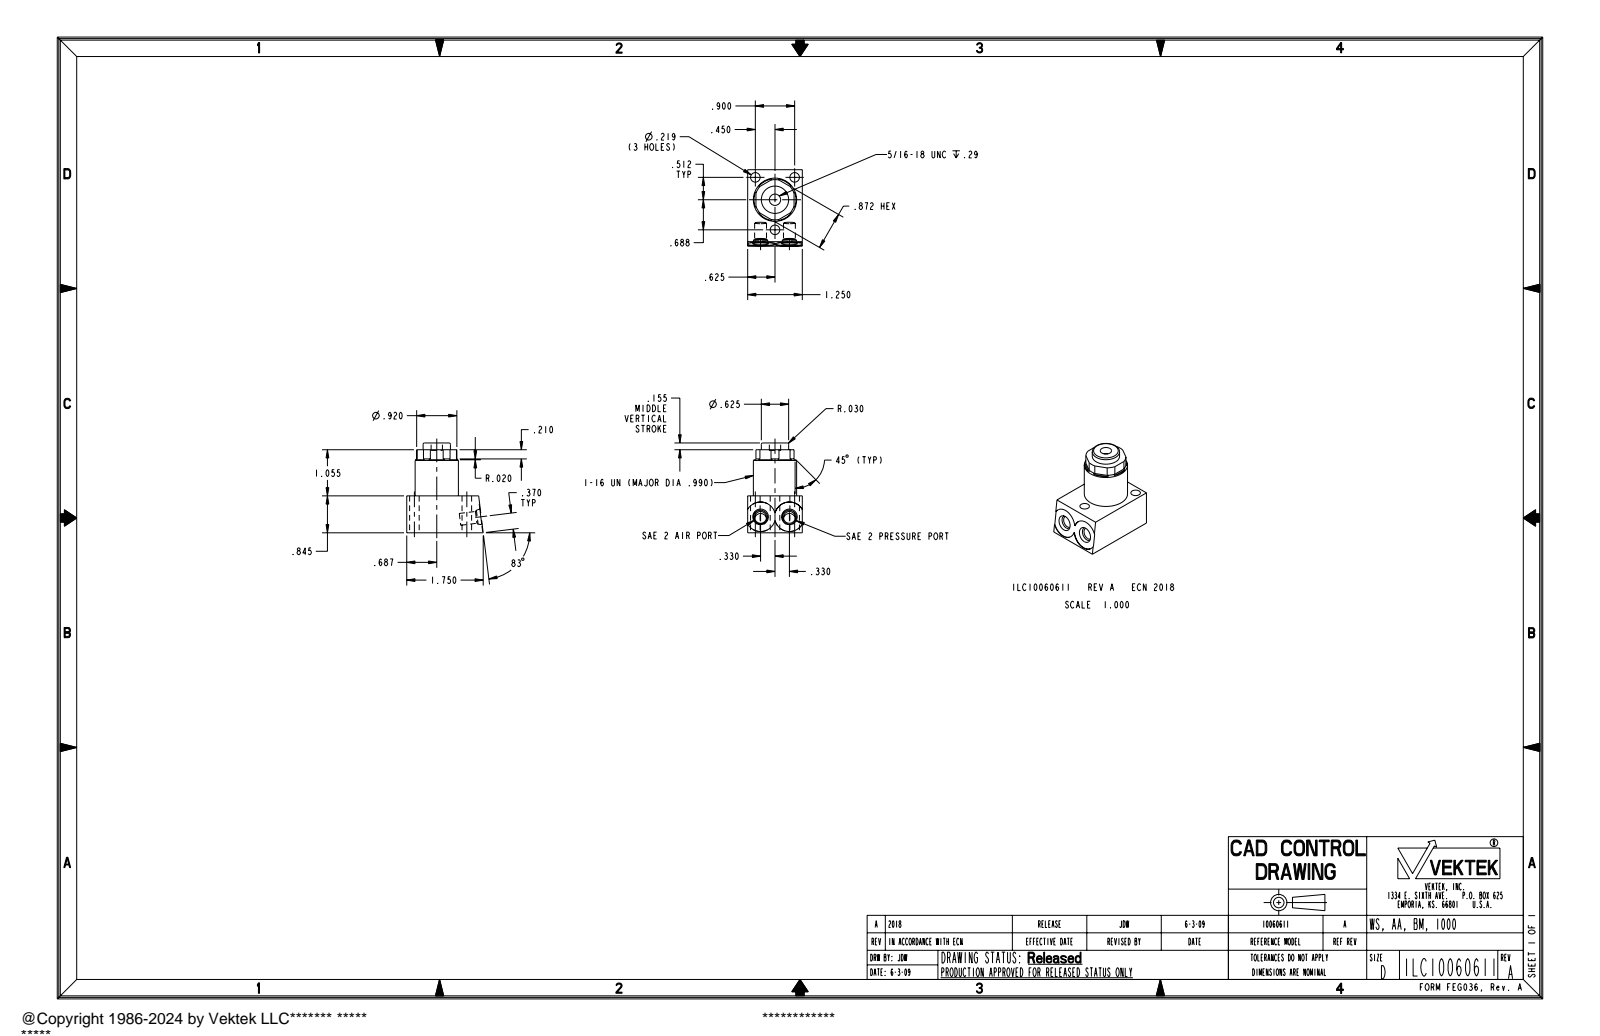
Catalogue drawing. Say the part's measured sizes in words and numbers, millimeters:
The part is named "ILC10060611". Its 3-D file was written by "PRO/ENGINEER BY PARAMETRIC TECHNOLOGY CORPORATION, 2007460 (AUTOMOTIVE_DESIGN_CC2)". It is 1 solid with 69 faces: 25 planar, 32 cylindrical and 12 other. Overall it measures 52.2 by 44.5 by 31.8 millimeters. Its volume is 40 130 cubic millimeters and its surface area 9 781 square millimeters. Round holes: 3 of diameter 5.6, 2 of diameter 6.9, 1 of diameter 6.6. Round bosses or shafts: 1 of diameter 25.1, 1 of diameter 15.9. Partial cylindrical surfaces (rounded edges, fillets, slot ends): 6 of radius 0.5, 2 of radius 8.7, 1 of radius 11.7. The main face-to-face distances are 31.8, 21.5, 48.3, 26.8, 52.2, 30.7, 3.9, 22.1, 4.8, 26.9. The hole center spacings are 17.3, 32.5, 16.8, 17.5, 22.9.
